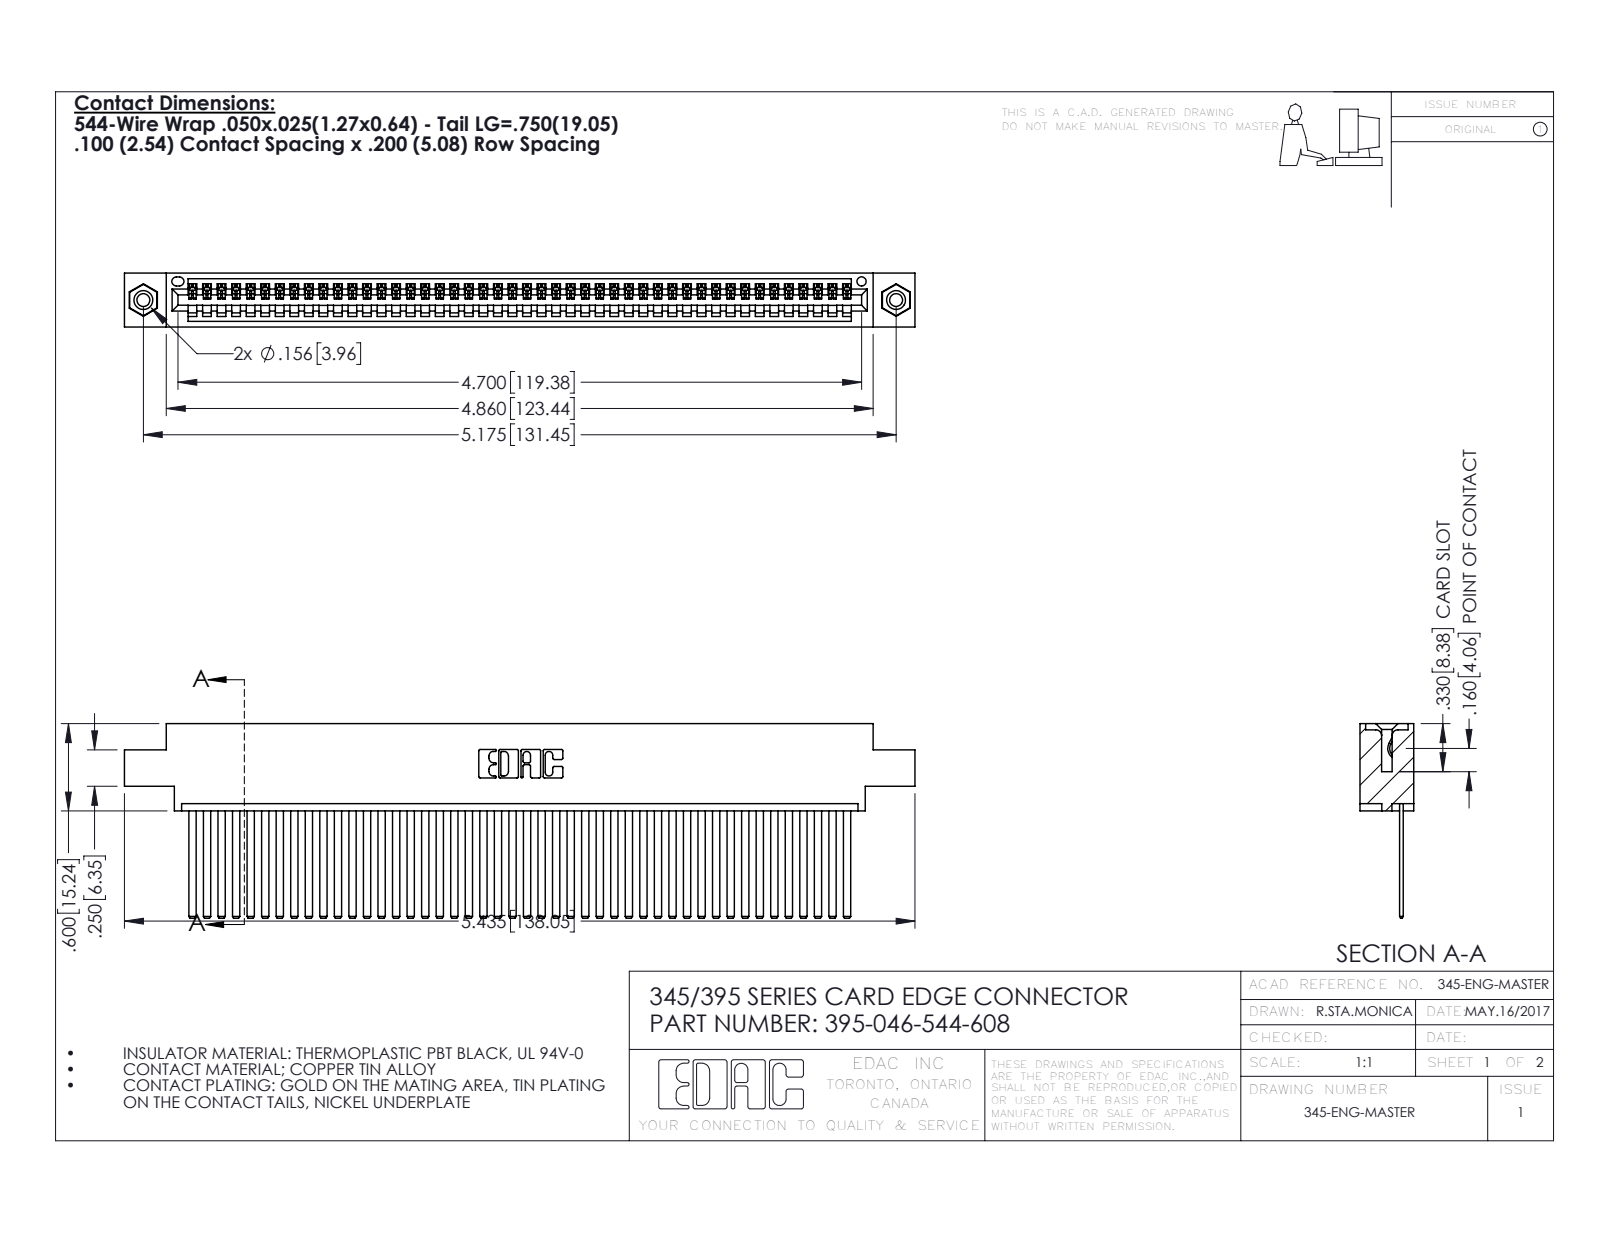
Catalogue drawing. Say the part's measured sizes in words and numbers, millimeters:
The part is named "395-046-544-608; 345-292-001_345-293-144; 345 Part_0.170 Offset - 0.156 Dia-TI; 345-250-001_345-250-003-102". Its 3-D file was written by "SolidWorks 2016 (CONFIG_CONTROL_DESIGN)". It is 49 solids with 2582 faces: 1772 planar, 794 cylindrical and 16 other. Overall it measures 138 by 34 by 9.4 millimeters. Its volume is 13 600 cubic millimeters and its surface area 19 820 square millimeters. Round holes: 2 of diameter 2.3, 2 of diameter 3.2, 2 of diameter 4, 1 of diameter 1.6. Round bosses or shafts: 2 of diameter 3.9. Partial cylindrical surfaces (rounded edges, fillets, slot ends): 92 of radius 0.2, 22 of radius 0.3, 6 of radius 0.2, 6 of radius 0.8, 3 of radius 0.7, 2 of radius 0.8, 2 of radius 1, 1 of radius 0.4. The main face-to-face distances are 1.8, 7.6, 0.6, 2.5, 6.9, 9.4, 5.1, 5.7, 4.4, 3.8. The hole center spacings are 6.9, 125.5, 131.4.
